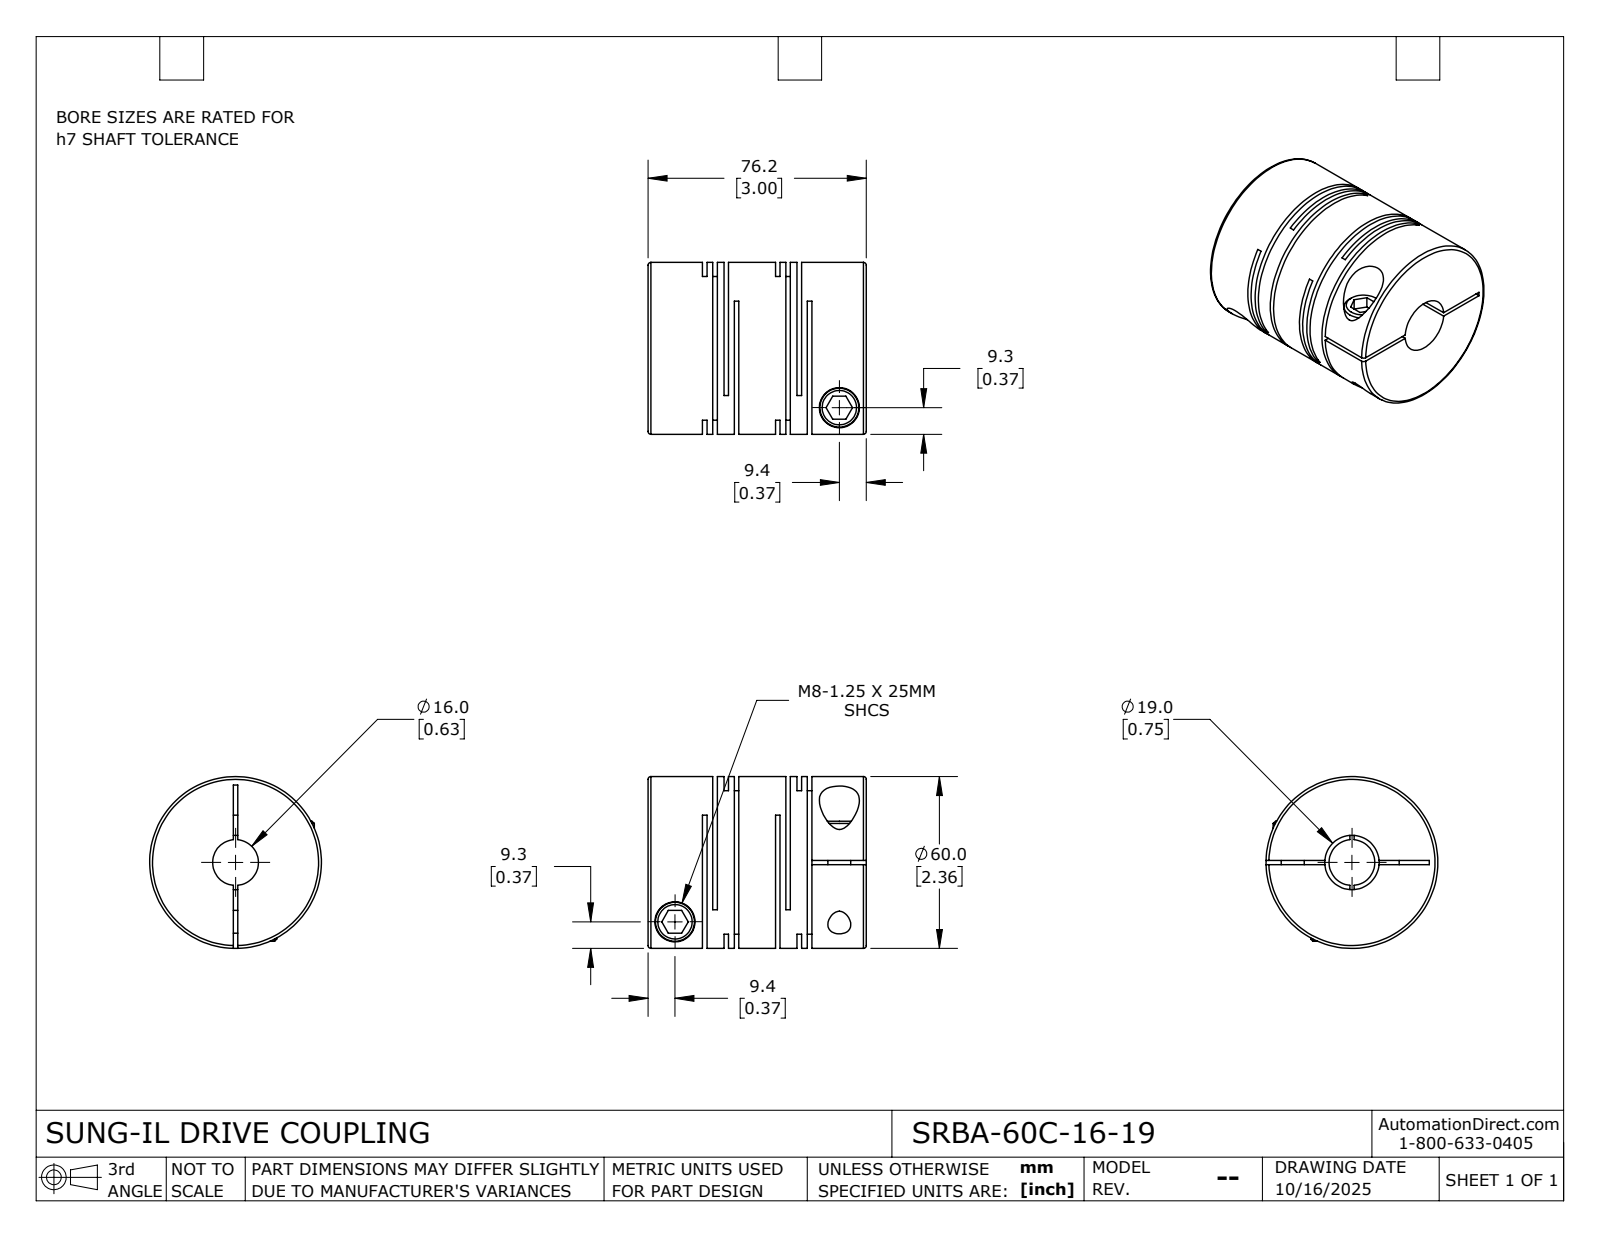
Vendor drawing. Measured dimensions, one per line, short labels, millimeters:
name: SRBA-60C-16-19
written by: SolidWorks 2024 (CONFIG_CONTROL_DESIGN)
unit: mm
bodies: 1 solid, 115 faces (60 planar, 42 cylindrical, 13 other)
size: 76.2 × 60 × 60
volume: 163 644 mm³; area: 59 635 mm²
holes: 2× ⌀8, 2× ⌀14, 1× ⌀16, 1× ⌀19
bosses: 2× ⌀13.6, 1× ⌀60
face distances: 1.6, 3.6, 7.5, 25.5, 33, 2, 5.9, 3.9, 23.9, 21.9
